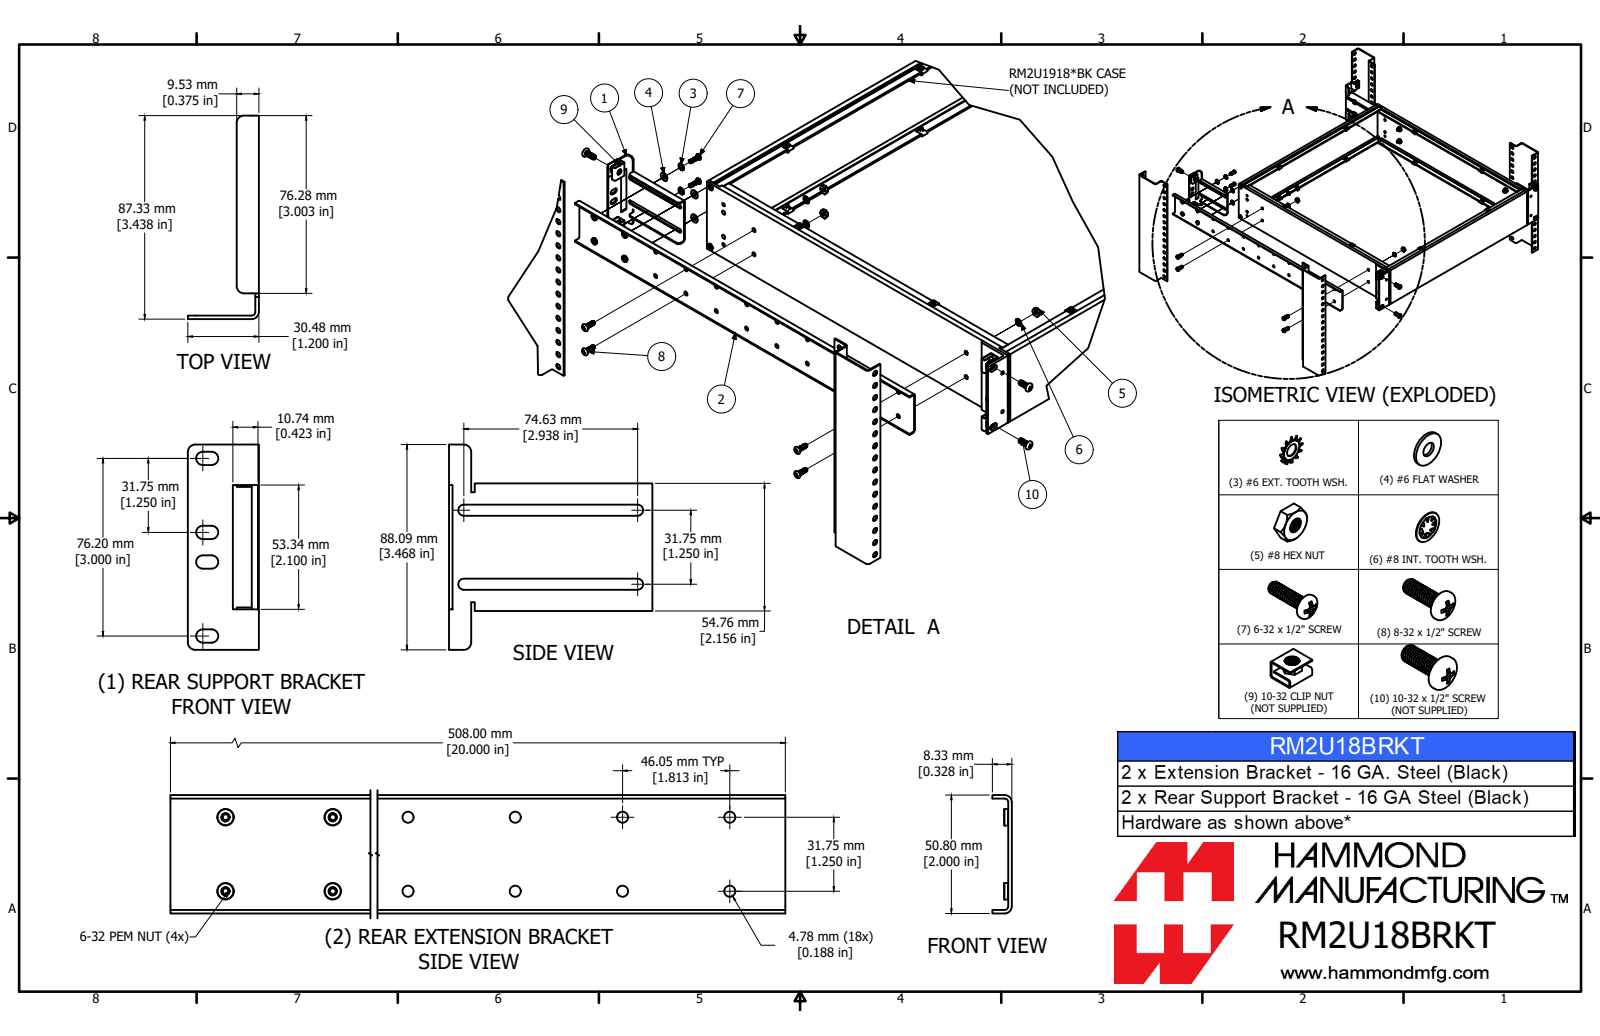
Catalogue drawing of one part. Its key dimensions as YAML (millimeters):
part_name: "RM2U18BRKT"
step_written_by: "SolidWorks 2021 (AUTOMOTIVE_DESIGN)"
units: millimeters
bodies: {solids: 6, faces: 734, planar: 494, cylindrical: 208, other: 32}
overall_size: [529.9, 88.1, 30.5]
volume: 58750
surface_area: 81550
round_holes:
  - {diameter: 4.8, count: 22}
  - {diameter: 2.5, count: 4}
  - {diameter: 3.5, count: 4}
round_bosses_or_shafts:
  - {diameter: 7.1, count: 4}
partial_cylinders:
  - {radius: 3.2, count: 6}
  - {radius: 1.5, count: 5}
  - {radius: 2.8, count: 5}
  - {radius: 3, count: 5}
  - {radius: 2.4, count: 4}
  - {radius: 2.7, count: 4}
  - {radius: 2.9, count: 3}
face_to_face_distances: [1.5, 49.3, 3, 50.8, 47.8, 2, 51.3, 9.9, 8.3, 6.8]
hole_center_spacings: [46.1, 55.9, 92.1, 97.4, 138.2, 141.8, 184.2, 186.9]
